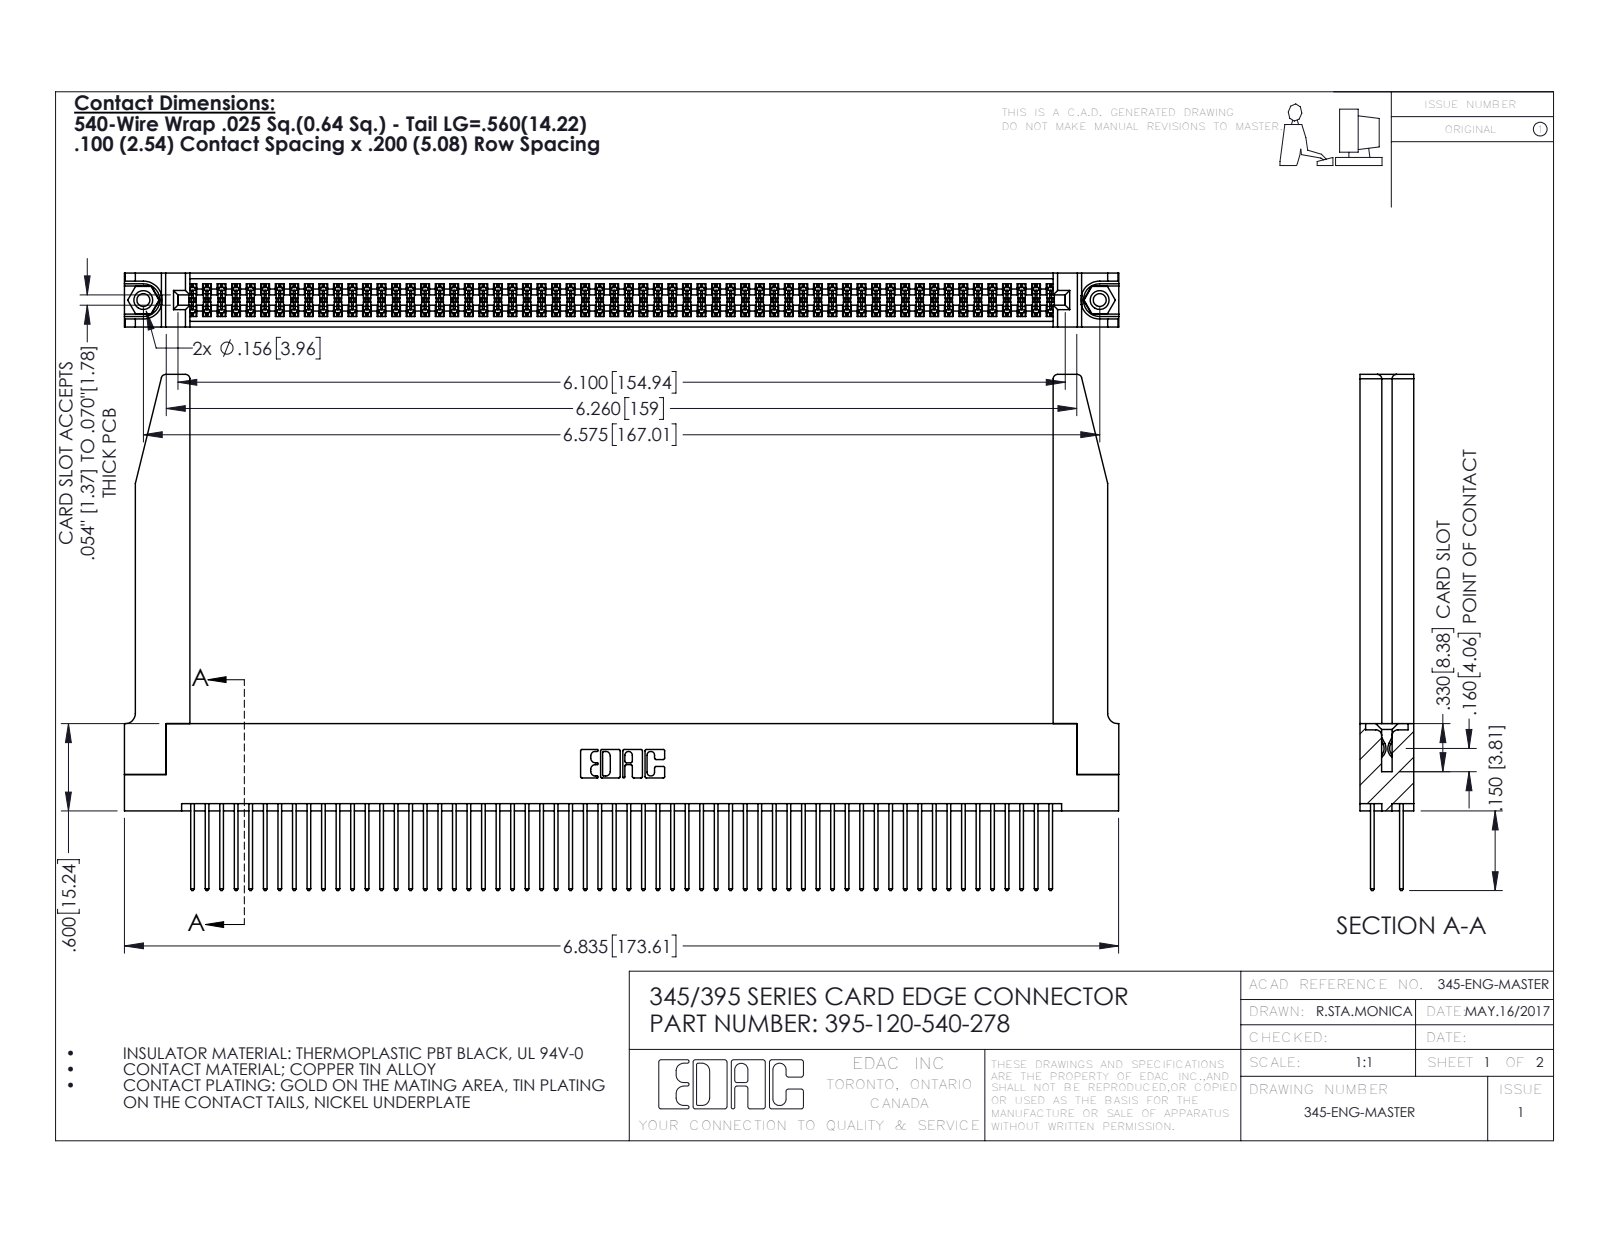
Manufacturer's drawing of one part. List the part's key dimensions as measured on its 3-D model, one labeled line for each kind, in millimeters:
Part name (STEP PRODUCT): 345-292-001_345-293-140; 345-220-078_345-220-078; 395-120-540-278; 345-250-001_345-250-001-102 (+1 more)
STEP written by: SolidWorks 2016 (CONFIG_CONTROL_DESIGN)
Units: millimetres
Bodies: 125 solids, 6360 faces (4182 planar, 2126 cylindrical, 52 other)
Overall size (bounding box): 173.6 × 90.1 × 9.4
Volume: 25 250 mm³ · Surface area: 35 150 mm²
Round holes (diameter × count): ⌀2.3 ×2, ⌀3.2 ×2, ⌀4 ×2, ⌀1.6 ×1
Round bosses / shafts (diameter × count): ⌀3.9 ×2
Partial cylindrical surfaces — rounded edges, fillets, slot ends (radius × count): R0.2 ×180, R0.3 ×120, R0.3 ×22, R0.8 ×8, R0.2 ×6, R0.8 ×6, R0.7 ×3, R0.4 ×2
Main face-to-face distances: 1.8, 7.6, 9.4, 5.1, 2.5, 6.9, 0.6, 5.7, 4.4, 3.8
Hole centre spacings: 6.9, 161, 167
